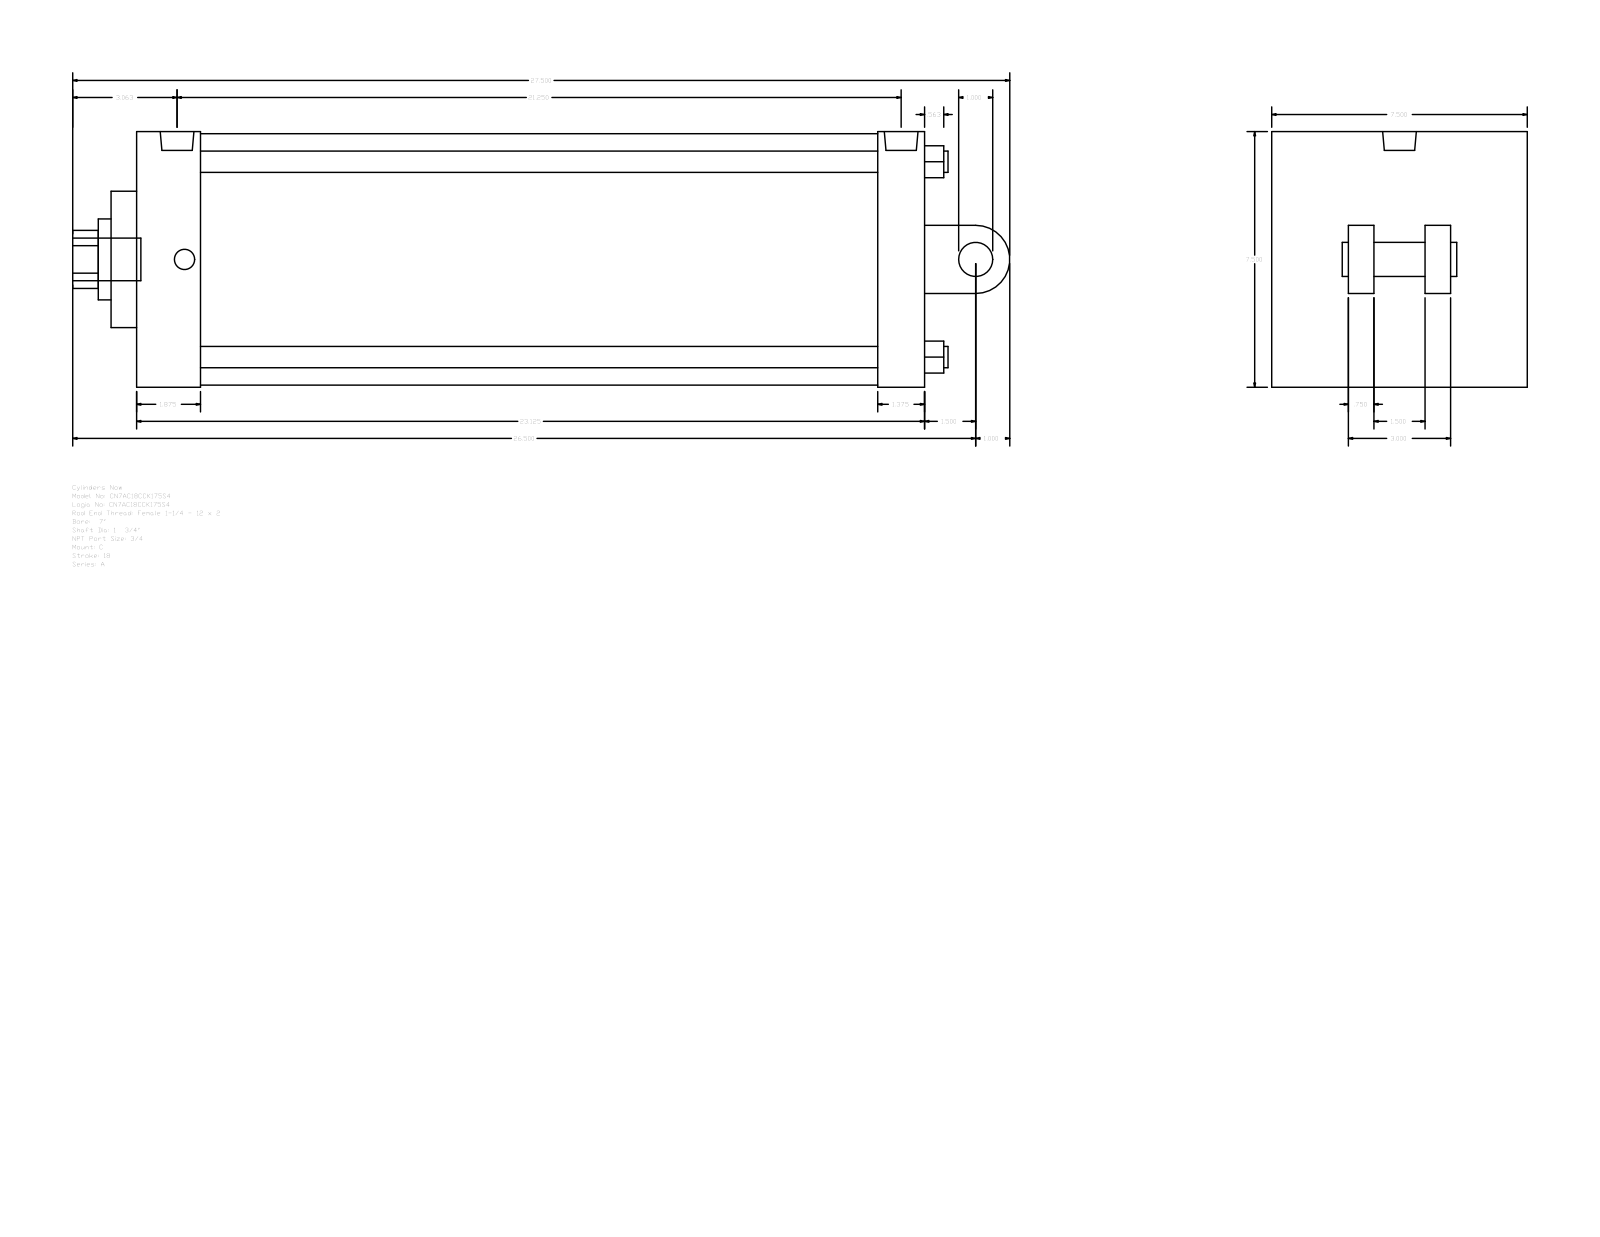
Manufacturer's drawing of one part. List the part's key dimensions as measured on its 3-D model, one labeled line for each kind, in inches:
Part name (STEP PRODUCT): A_C__0700_1.75
STEP written by: GSSL Pune (CONFIG_CONTROL_DESIGN)
Units: inches
Bodies: 0 solids, 104 faces (75 planar, 29 cylindrical, 0 other)
Overall size (bounding box): 27.5 × 7.5 × 7.5
Round holes (diameter × count): ⌀0.625 ×4, ⌀0.594 ×2, ⌀0.989 ×1, ⌀1.75 ×1, ⌀2.375 ×1, ⌀7.375 ×1
Round bosses / shafts (diameter × count): ⌀0.594 ×2, ⌀1.25 ×1, ⌀1 ×1, ⌀0.989 ×1
Partial cylindrical surfaces — rounded edges, fillets, slot ends (radius × count): R0.852 ×1, R1 ×1
Main face-to-face distances: 7.5, 23.125, 0.75, 3, 2.25, 1.75, 1.375, 1.875, 21.25, 21.75
Hole centre spacings: 4.052, 5.73, 8.103, 0.219
